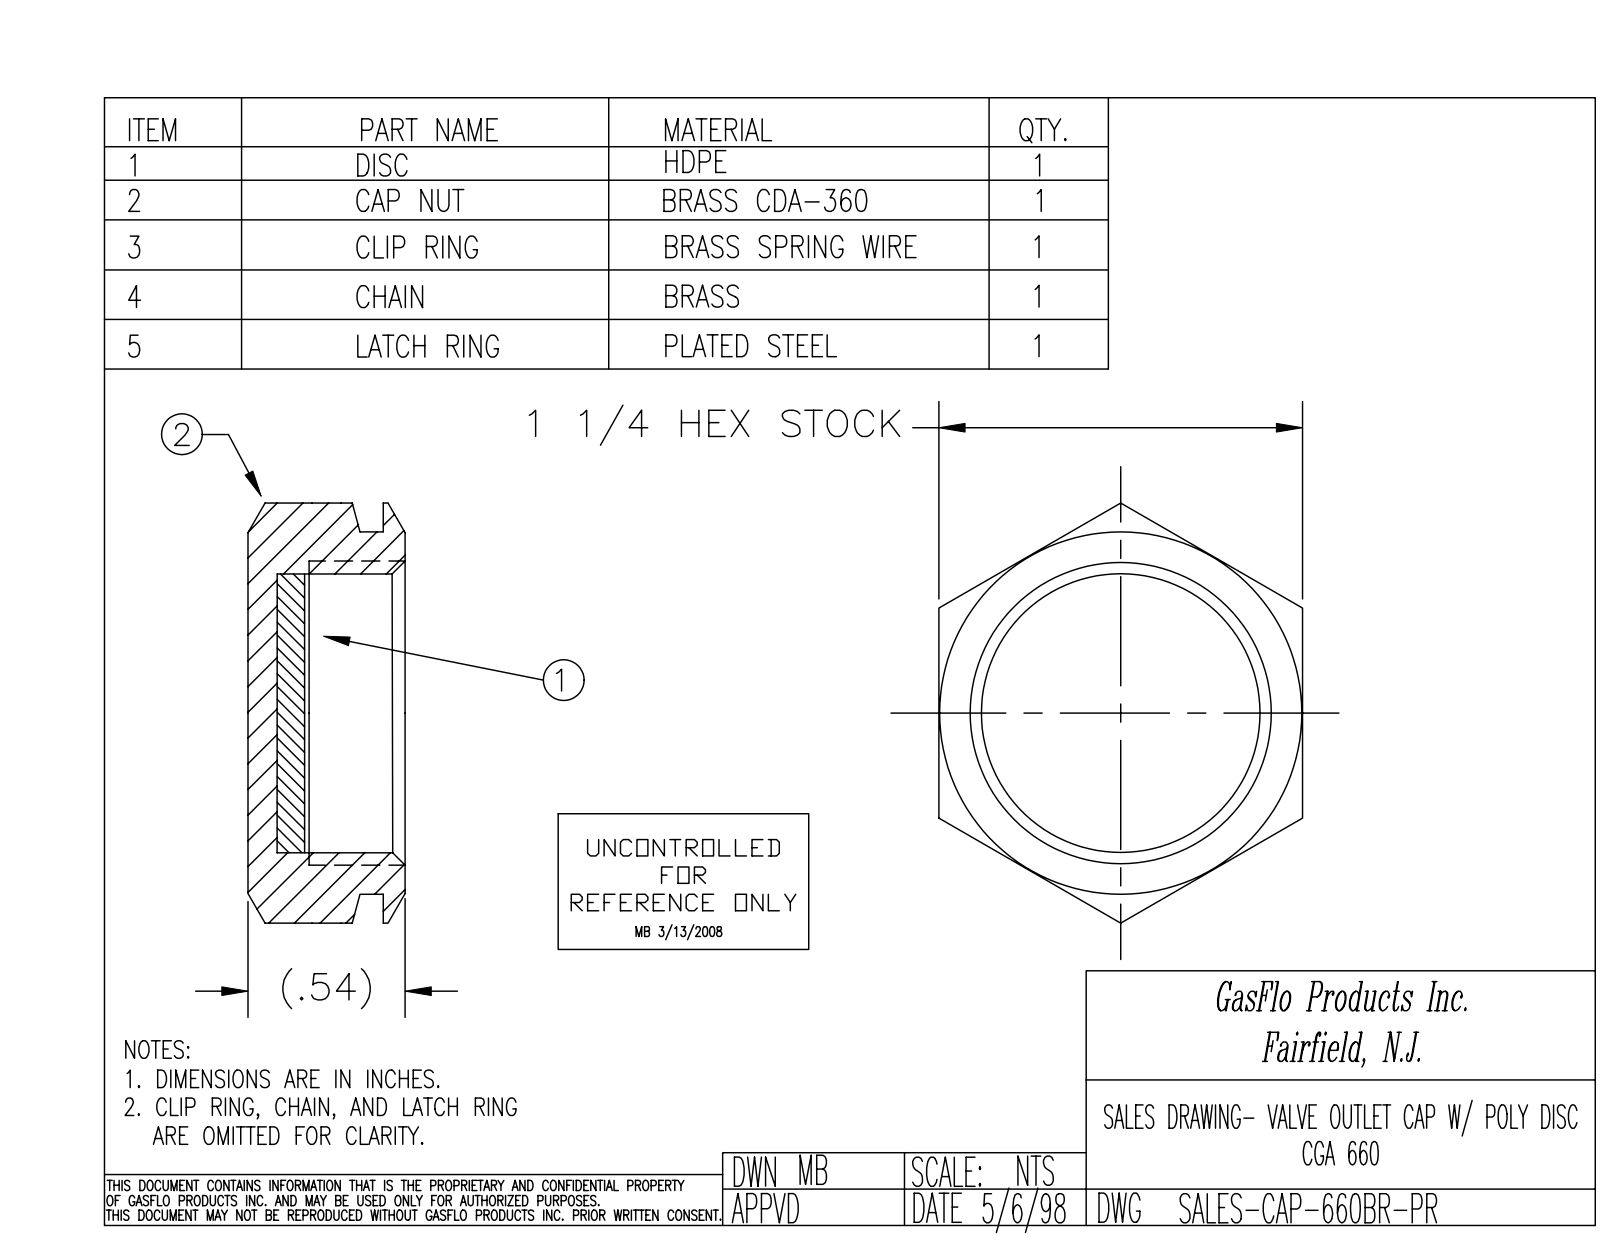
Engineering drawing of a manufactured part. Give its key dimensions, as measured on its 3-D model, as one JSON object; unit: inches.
{"part_name": "PRT-004002; PRT-002255_SMALL PIN; PRT-002285; ASY-000291 (+5 more)", "step_written_by": "SolidWorks 2018 (CONFIG_CONTROL_DESIGN)", "units": "inches", "bodies": {"solids": 13, "faces": 304, "planar": 56, "cylindrical": 117, "other": 131}, "overall_size": [4.139, 1.965, 1.555], "volume_in3": 0.536, "surface_area_in2": 13.6, "round_holes": [[0.063, 1], [0.962, 1]], "round_bosses_or_shafts": [[0.063, 30], [1.243, 1], [0.963, 1], [0.1, 1]], "partial_cylinders_radius": [[0.005, 24], [0.25, 4], [0.01, 2]], "face_to_face_distances": [0.1, 1.25, 0.094, 0.194, 0.346, 0.44, 0.54, 0.073, 0.273, 0.367], "hole_center_spacings": [0.478]}
